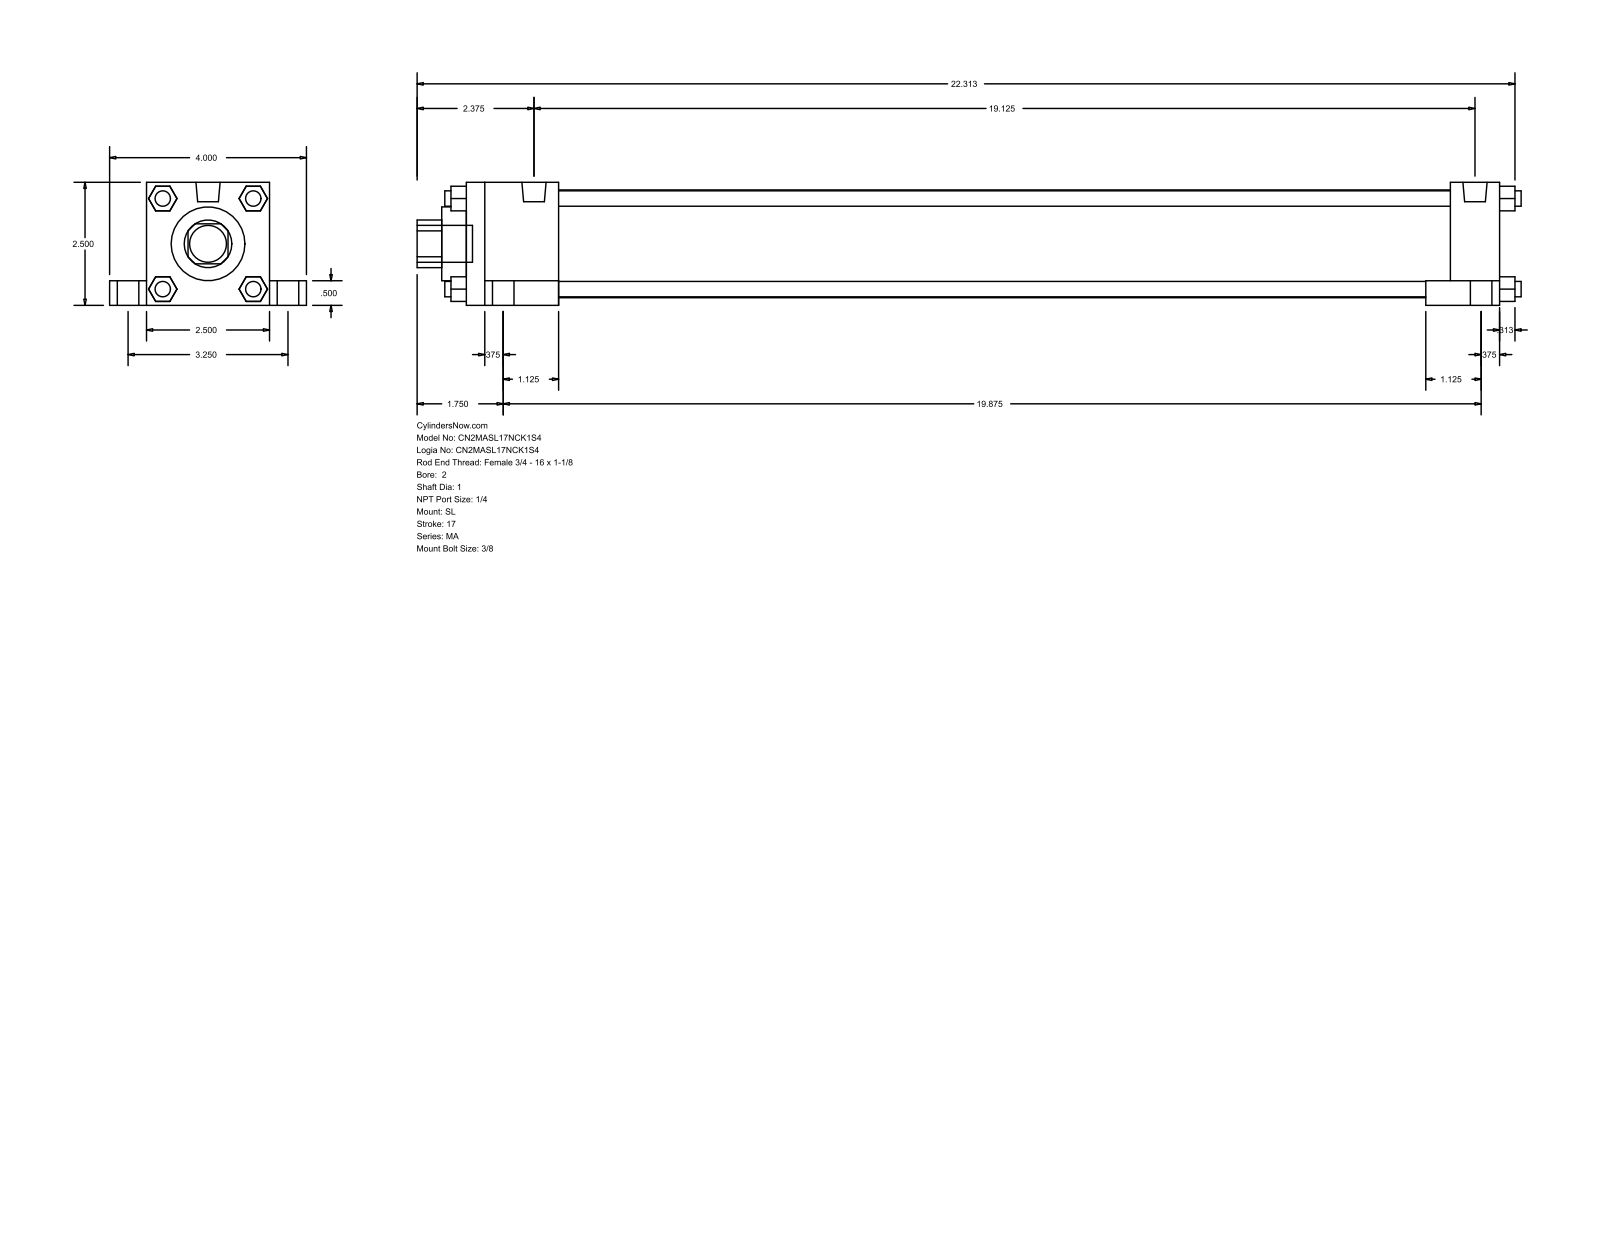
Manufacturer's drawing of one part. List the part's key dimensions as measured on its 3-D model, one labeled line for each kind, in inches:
Part name (STEP PRODUCT): MA_SL__0200_1
STEP written by: GSSL Pune (CONFIG_CONTROL_DESIGN)
Units: inches
Bodies: 0 solids, 148 faces (112 planar, 36 cylindrical, 0 other)
Overall size (bounding box): 22.437 × 4 × 2.5
Round holes (diameter × count): ⌀1 ×1, ⌀1.5 ×1, ⌀2.19 ×1
Round bosses / shafts (diameter × count): ⌀0.313 ×8, ⌀0.687 ×4, ⌀0.437 ×4, ⌀0.492 ×2, ⌀0.75 ×1
Partial cylindrical surfaces — rounded edges, fillets, slot ends (radius × count): R0.484 ×1
Main face-to-face distances: 2.5, 0.5, 21, 0.75, 3.25, 1, 2, 1.875, 19.125, 20
